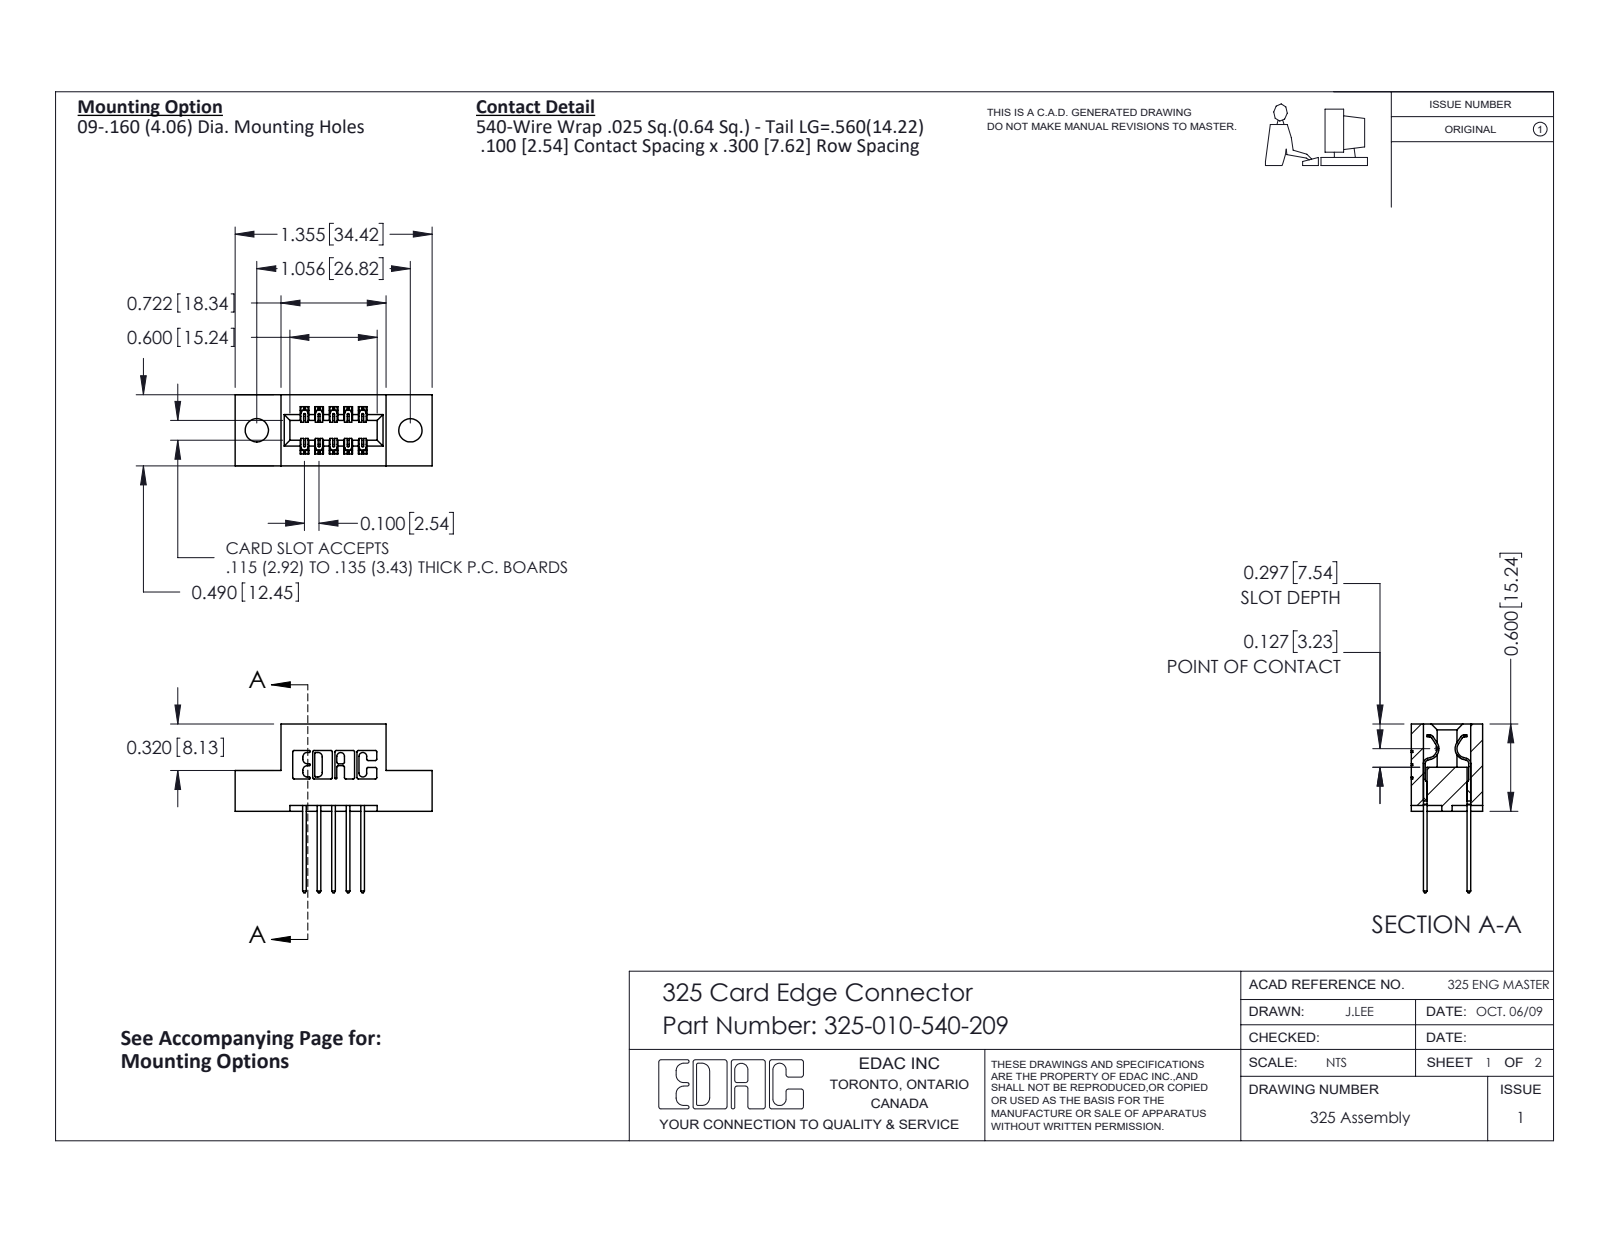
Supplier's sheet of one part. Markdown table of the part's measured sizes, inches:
| quantity | value |
| --- | --- |
| part name | 325-010-540-209; 325 Part_.160 TH; 325-292-001_325-293-140 |
| STEP written by | SolidWorks 2016 (CONFIG_CONTROL_DESIGN) |
| units | inches |
| bodies | 11 solids, 634 faces (430 planar, 204 cylindrical, 0 other) |
| overall size | 1.355 × 1.16 × 0.49 |
| volume | 0.239 in³ |
| surface area | 6.147 in² |
| round holes (diameter × count) | 0.16 × 2 |
| partial cylindrical surfaces (radius × count) | 0.01 × 22, 0.006 × 15, 0.01 × 10, 0.007 × 6, 0.031 × 6, 0.026 × 3, 0.014 × 2, 0.022 × 2 |
| main face-to-face distances | 0.083, 0.3, 0.407, 0.1, 0.49, 0.04, 0.2, 0.383, 0.107, 0.025 |
| hole center spacings | 1.056 |
